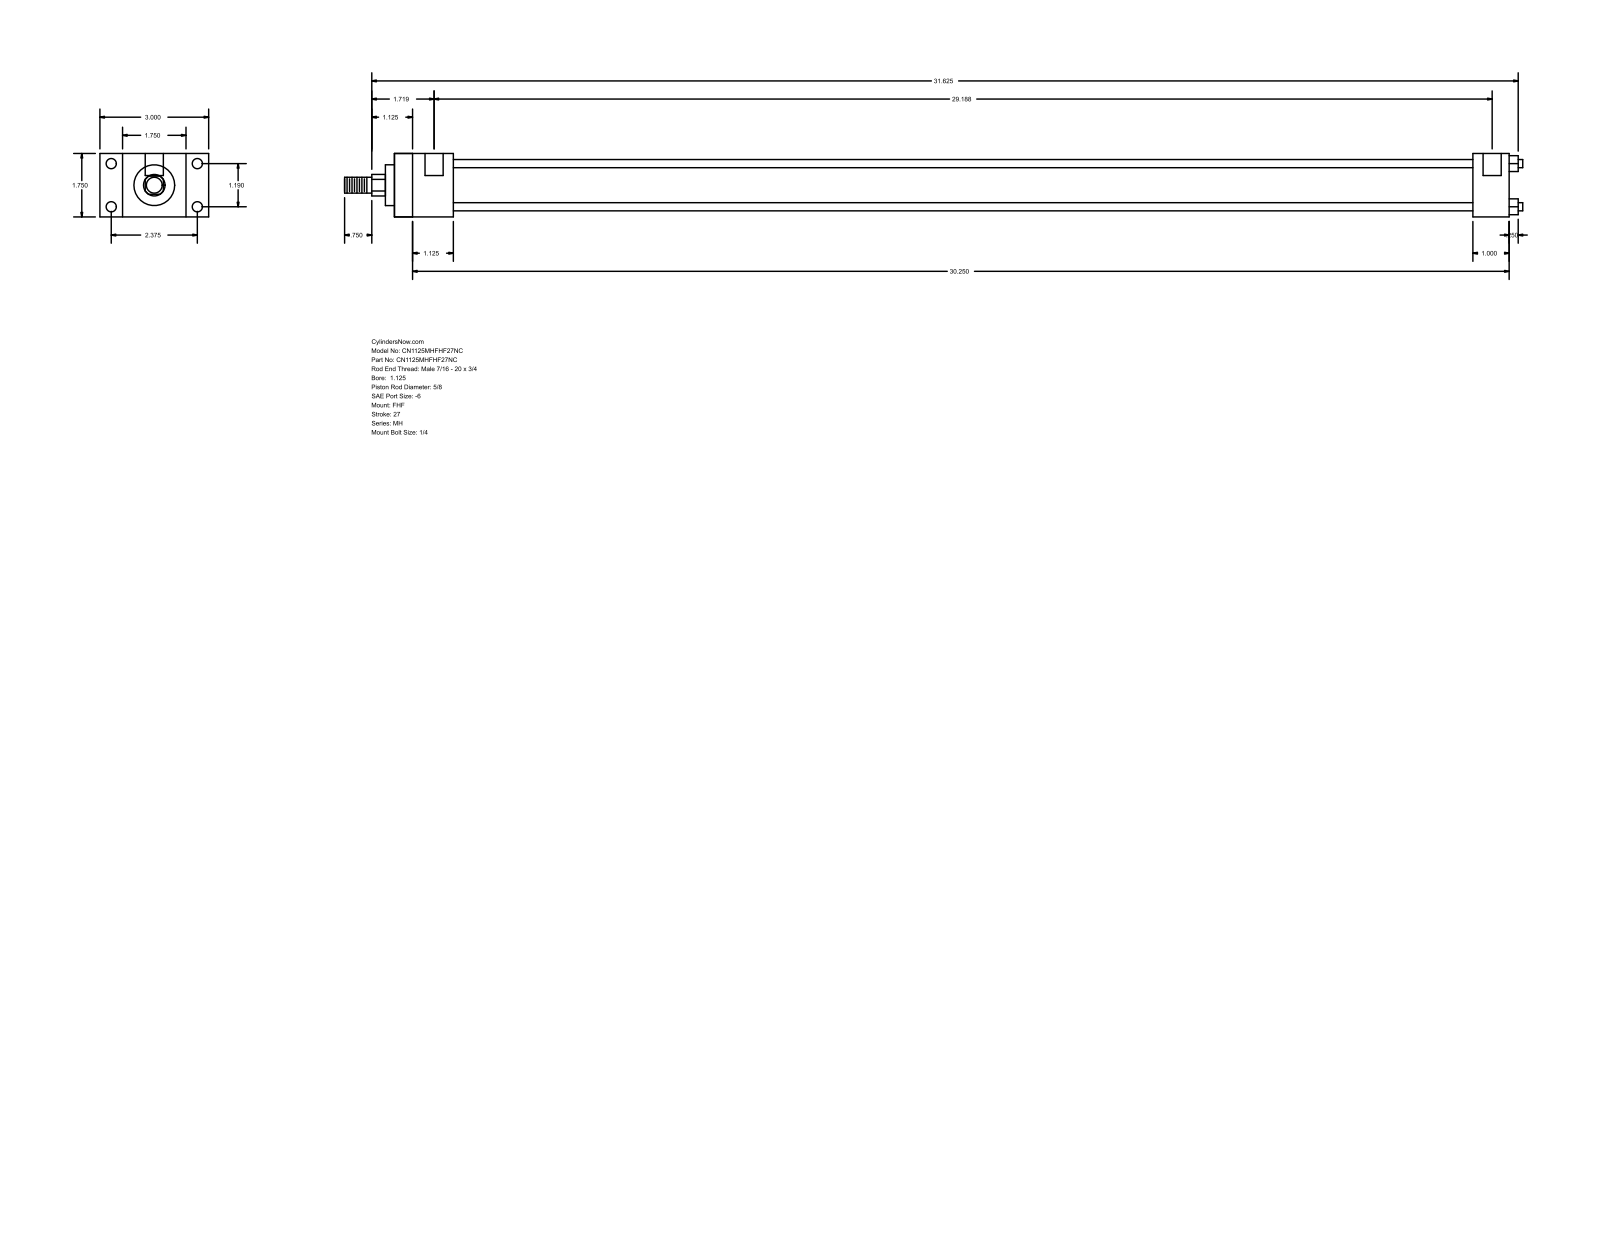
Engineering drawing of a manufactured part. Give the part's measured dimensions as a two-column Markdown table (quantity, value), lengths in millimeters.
| quantity | value |
| --- | --- |
| part name | MH_FHF__0112_0.625 |
| STEP written by | GSSL Pune (CONFIG_CONTROL_DESIGN) |
| units | millimeters |
| bodies | 0 solids, 88 faces (60 planar, 28 cylindrical, 0 other) |
| overall size | 825.5 × 76.2 × 44.45 |
| round holes (diameter × count) | 5.56 × 4, 7.14 × 4, 12.7 × 2 |
| round bosses / shafts (diameter × count) | 5.71 × 4, 34.92 × 1, 28.57 × 1, 15.88 × 1, 11.11 × 1 |
| partial cylindrical surfaces (radius × count) | 7.54 × 1 |
| main face-to-face distances | 44.46, 15.87, 60.33, 41.27, 76.2, 781.04, 739.77, 25.4, 755.64, 714.37 |
| hole center spacings | 30.22, 60.32, 67.47, 738.19, 3.17, 741.36 |
